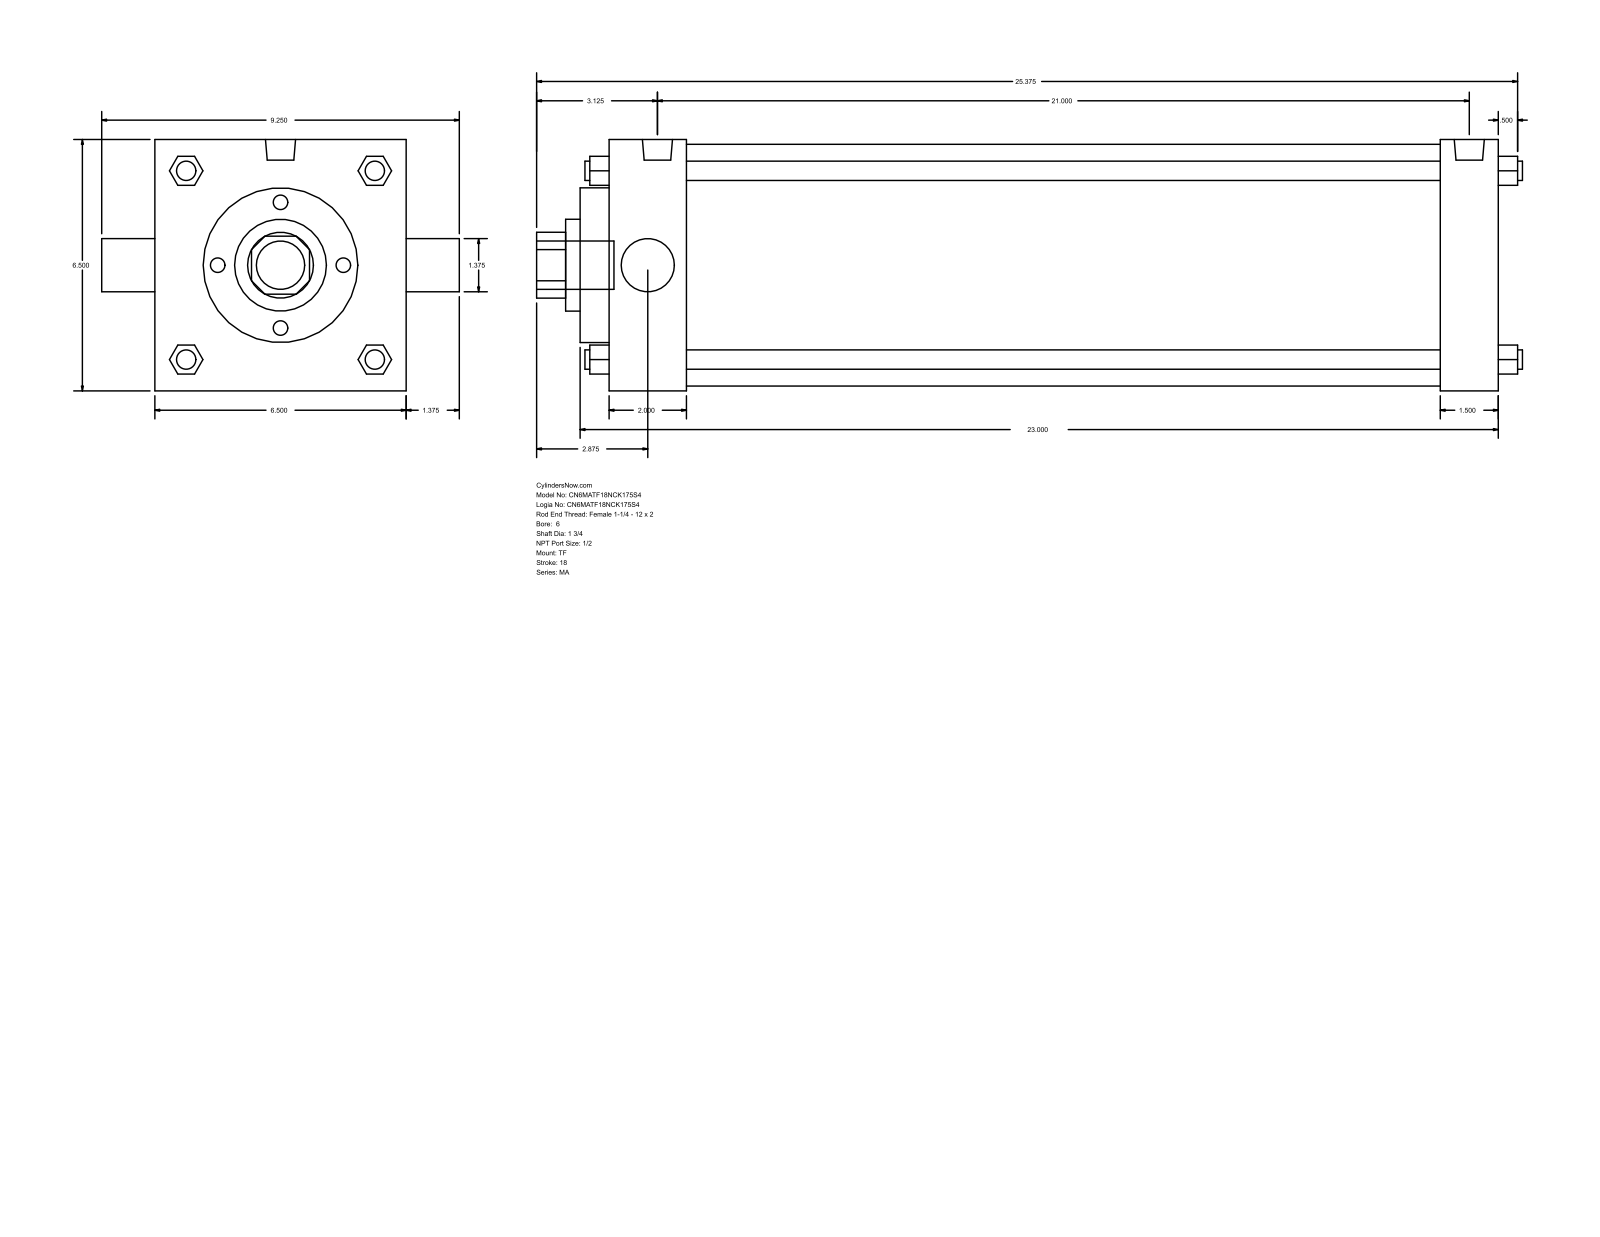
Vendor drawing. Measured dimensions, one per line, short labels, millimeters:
name: MA_TF__0600_1.75
written by: GSSL Pune (CONFIG_CONTROL_DESIGN)
unit: mm
bodies: 0 solids, 122 faces (93 planar, 29 cylindrical, 0 other)
size: 647.7 × 234.95 × 165.1
holes: 1× ⌀34.92, 1× ⌀44.45, 1× ⌀60.33, 1× ⌀101.6, 1× ⌀158.75
bosses: 4× ⌀12.7, 3× ⌀17.46, 2× ⌀19.77, 1× ⌀31.75
rounds: 1× R21.63
face distances: 165.1, 584.21, 19.05, 38.1, 50.8, 533.41, 546.11, 495.31, 69.85, 565.16
